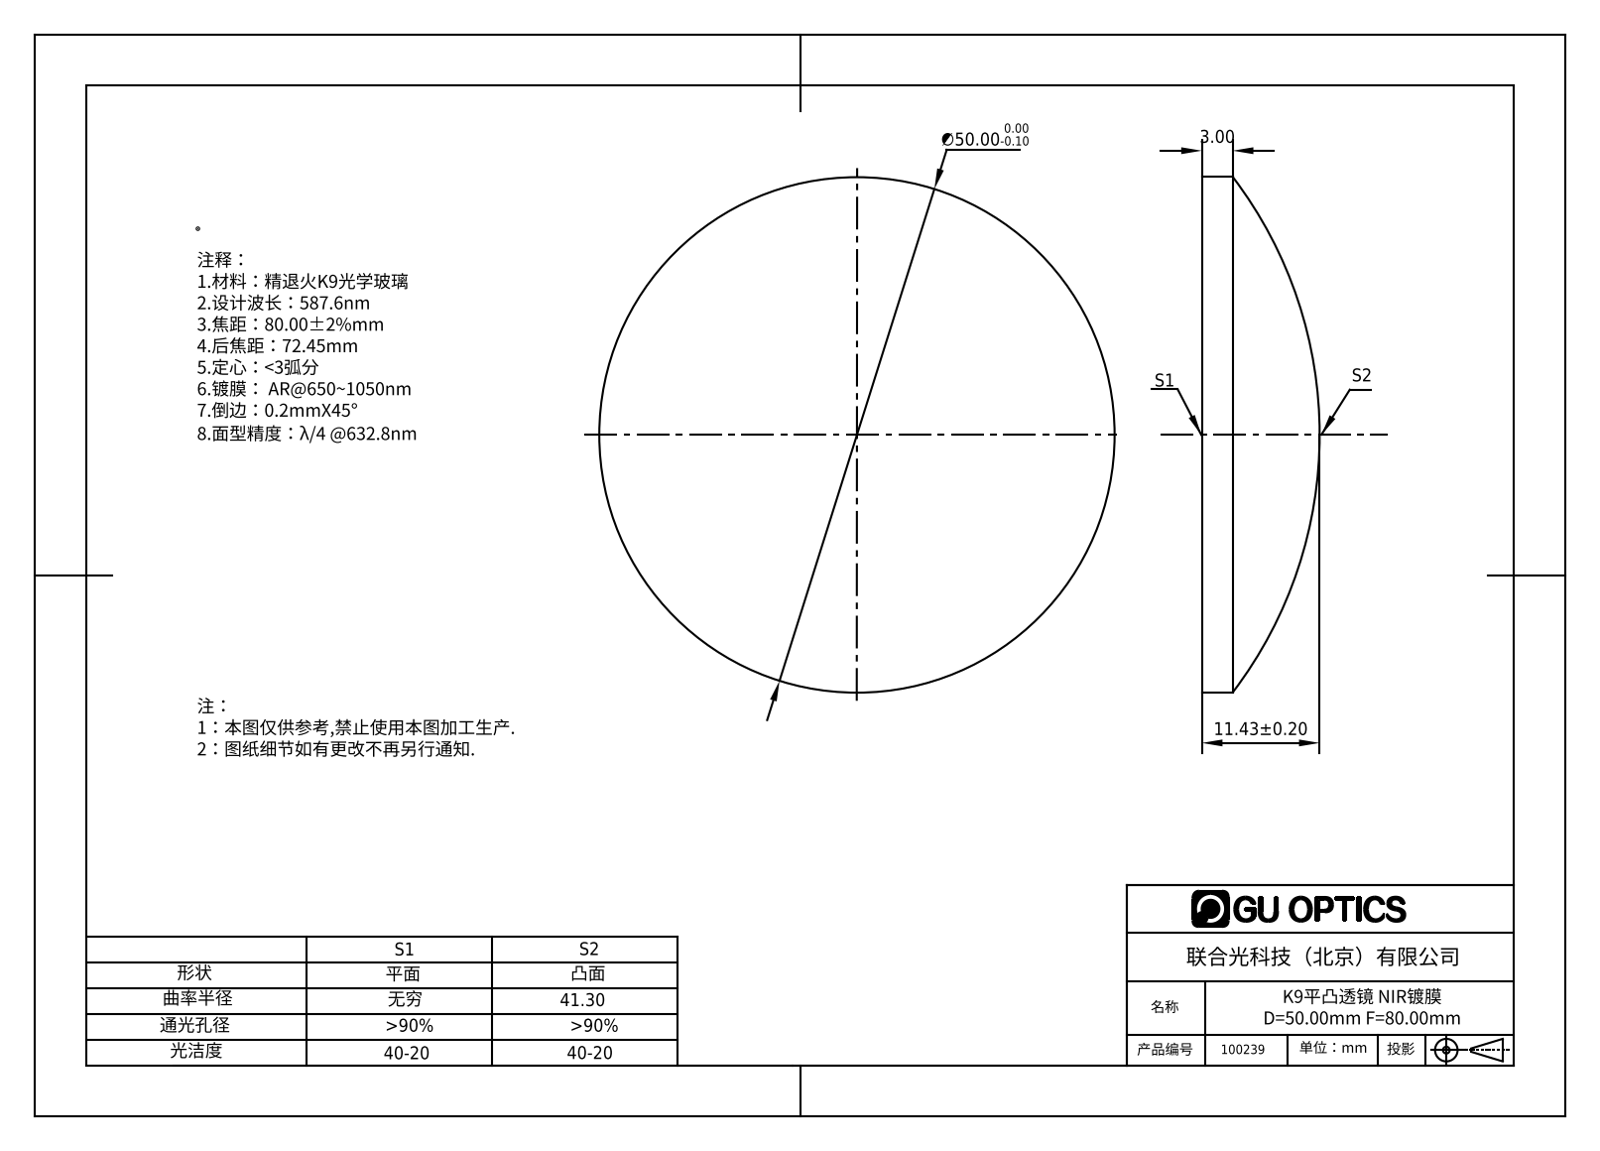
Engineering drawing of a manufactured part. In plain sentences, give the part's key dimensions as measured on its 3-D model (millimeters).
The part is named "100239". Its 3-D file was written by "SolidWorks 2016 (AUTOMOTIVE_DESIGN)". It is 1 solid with 5 faces: 1 planar, 2 cylindrical and 2 other. Overall it measures 50 by 50 by 11.43 millimeters. Its volume is 14 480 cubic millimeters and its surface area 4 621 square millimeters. Round bosses or shafts: 1 of diameter 50.
